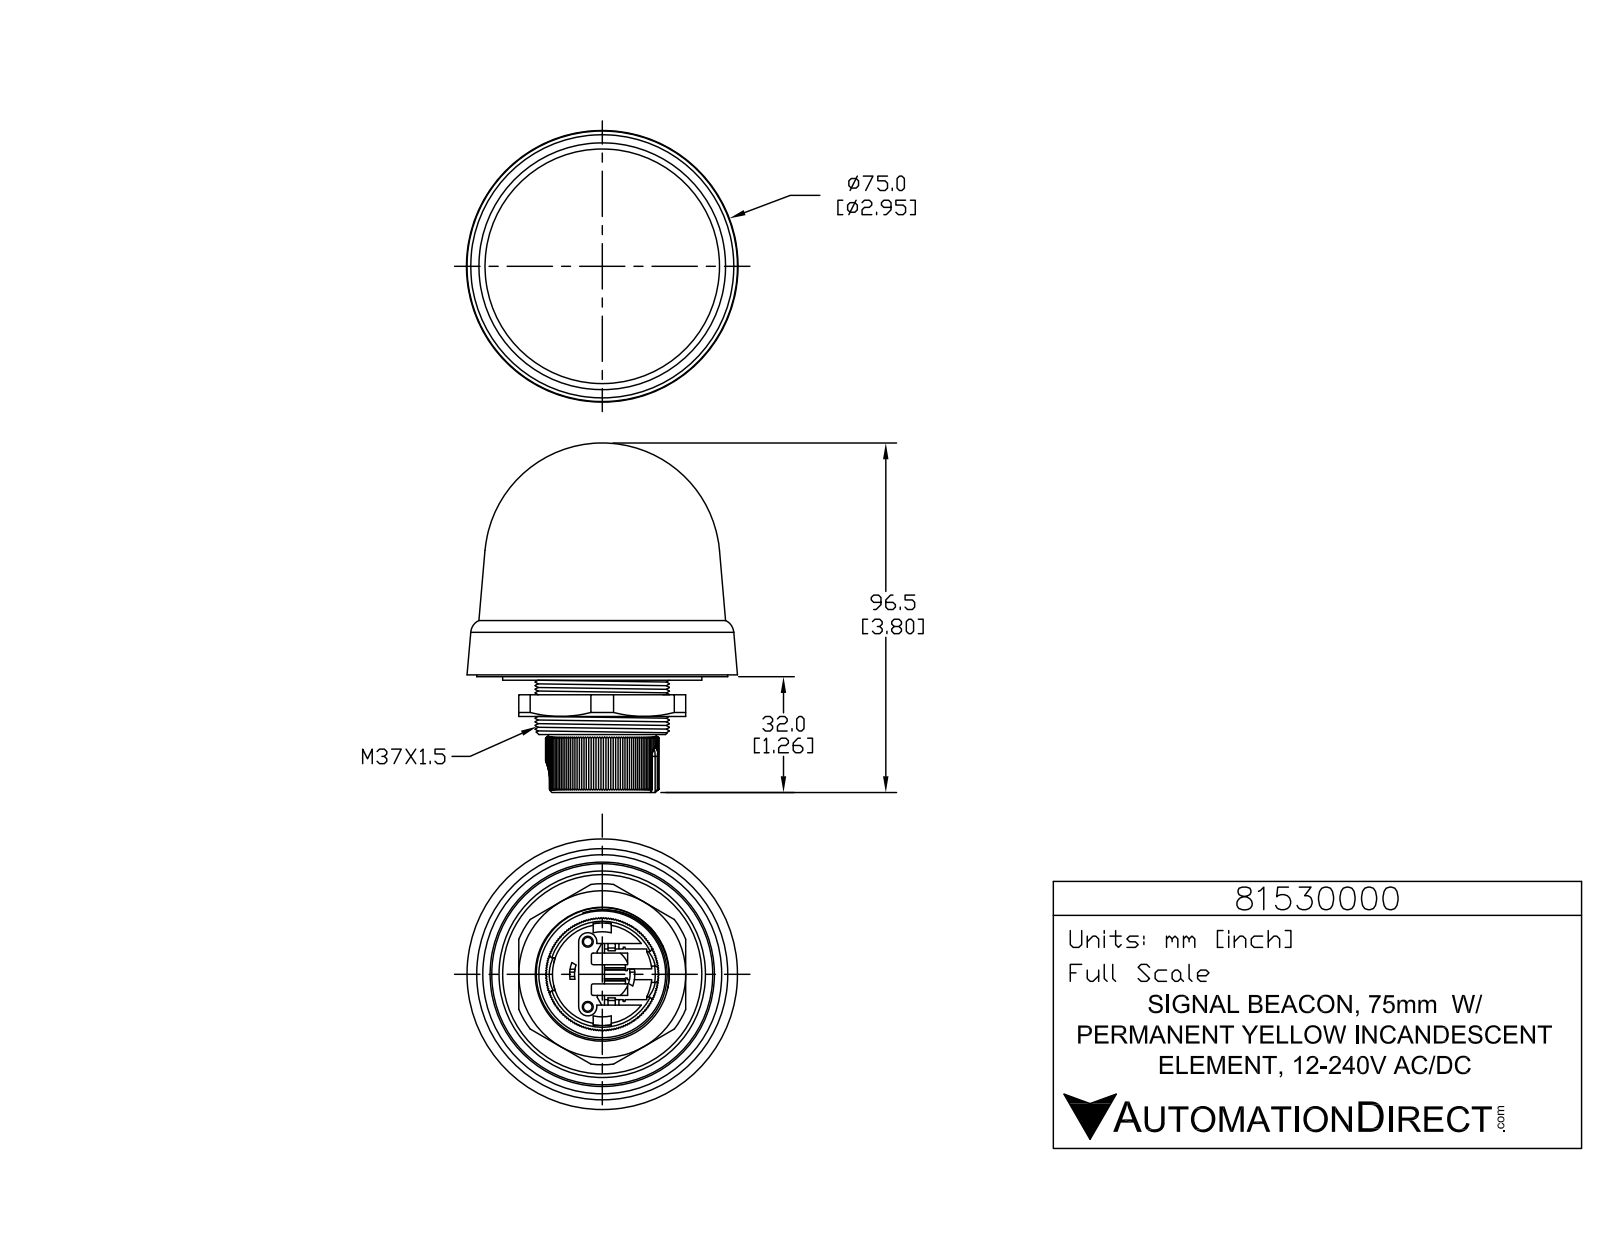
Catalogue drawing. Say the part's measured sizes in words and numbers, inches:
The part is named "81530000". Its 3-D file was written by "SolidWorks 2019 (CONFIG_CONTROL_DESIGN)". It is 3 solids with 560 faces: 432 planar, 80 cylindrical and 48 other. Overall it measures 3.799 by 2.941 by 2.941 inches. Its volume is 12.36 cubic inches and its surface area 58.68 square inches. Round holes: 2 of diameter 0.094, 2 of diameter 0.118, 1 of diameter 0.604, 1 of diameter 1.142. Round bosses or shafts: 2 of diameter 0.217, 2 of diameter 0.067, 1 of diameter 2.165, 1 of diameter 1.457, 1 of diameter 0.925. Partial cylindrical surfaces (rounded edges, fillets, slot ends): 6 of radius 0.008, 6 of radius 0.039, 4 of radius 0.02, 2 of radius 0.031, 2 of radius 0.079, 2 of radius 0.098, 1 of radius 0.177, 1 of radius 0.354. The main face-to-face distances are 0.177, 0.354, 0.197, 0.433, 0.512, 0.335, 0.059, 0.394, 0.118, 0.157. The hole center spacings are 0.388, 0.709.
